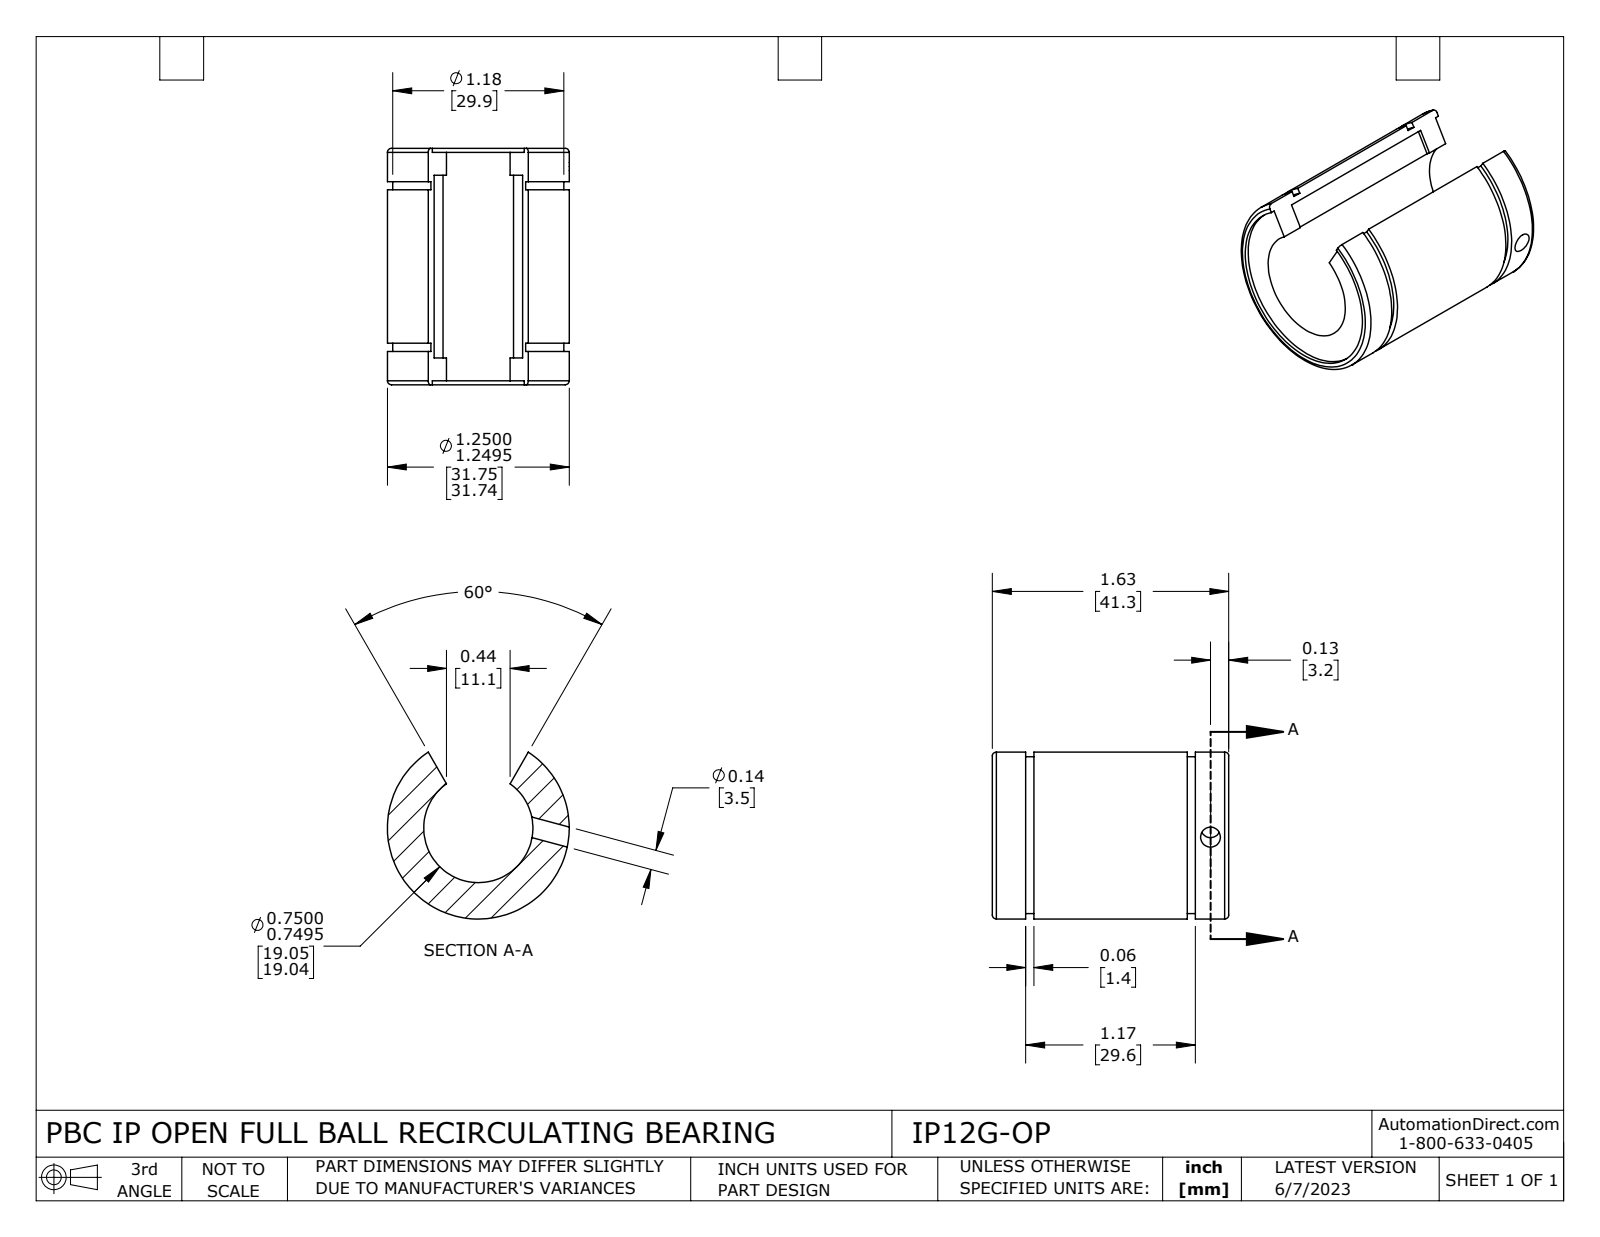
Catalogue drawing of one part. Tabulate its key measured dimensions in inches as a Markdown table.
| quantity | value |
| --- | --- |
| part name | IP12G-OP |
| STEP written by | SolidWorks 2021 (CONFIG_CONTROL_DESIGN) |
| units | inches |
| bodies | 1 solid, 40 faces (16 planar, 20 cylindrical, 4 other) |
| overall size | 1.625 × 1.25 × 1.147 |
| volume | 0.977 in³ |
| surface area | 10.84 in² |
| round holes (diameter × count) | 0.136 × 1, 0.75 × 1, 1.138 × 1 |
| round bosses / shafts (diameter × count) | 1.25 × 1, 1.176 × 1 |
| partial cylindrical surfaces (radius × count) | 0.545 × 1 |
| main face-to-face distances | 1.569, 0.03, 0.202, 1.367, 0.258, 1.311, 0.056, 1.109, 0.028, 0.23 |
